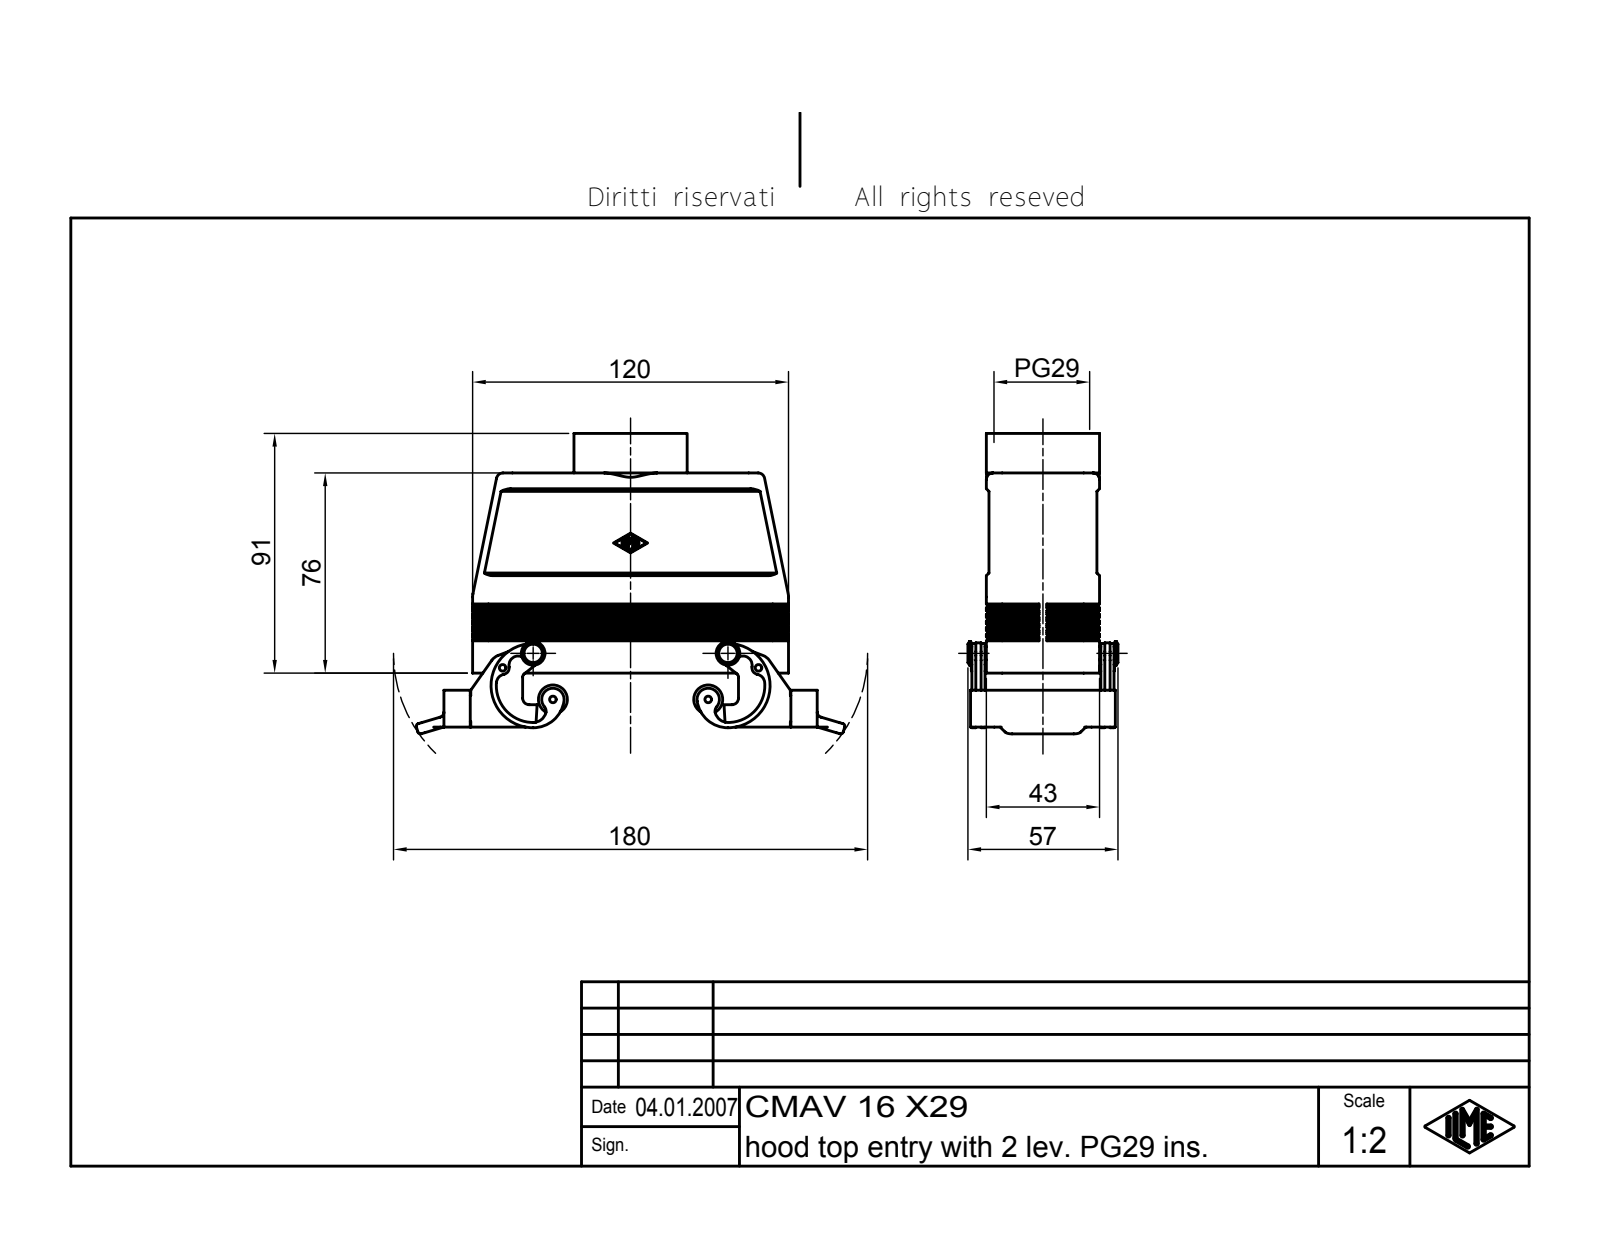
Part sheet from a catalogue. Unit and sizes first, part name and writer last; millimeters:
Units: millimetres
Overall size (bounding box): 162.79 × 114.08 × 57
Round holes (diameter × count): ⌀2.5 ×2, ⌀33.48 ×1, ⌀35.48 ×1
Round bosses / shafts (diameter × count): ⌀11 ×2, ⌀9 ×2, ⌀5 ×2, ⌀2 ×2, ⌀43 ×1, ⌀34.48 ×1
Partial cylindrical surfaces — rounded edges, fillets, slot ends (radius × count): R0.25 ×14, R1 ×12, R2 ×10, R2.5 ×10, R6 ×10, R3 ×8, R3.5 ×4, R5 ×4
Main face-to-face distances: 3, 2, 42, 37, 40, 1, 39, 43, 41, 9
Hole centre spacings: 97.2
Volume: 108 405 mm³ · Surface area: 72 901 mm²
Bodies: 1 solid, 945 faces (282 planar, 248 cylindrical, 415 other)
Part name (STEP PRODUCT): CAV Tüllengehäuse 2 Bügel für einen Einsatz Teil A
STEP written by: Autodesk Inventor 7 (AUTOMOTIVE_DESIGN)
